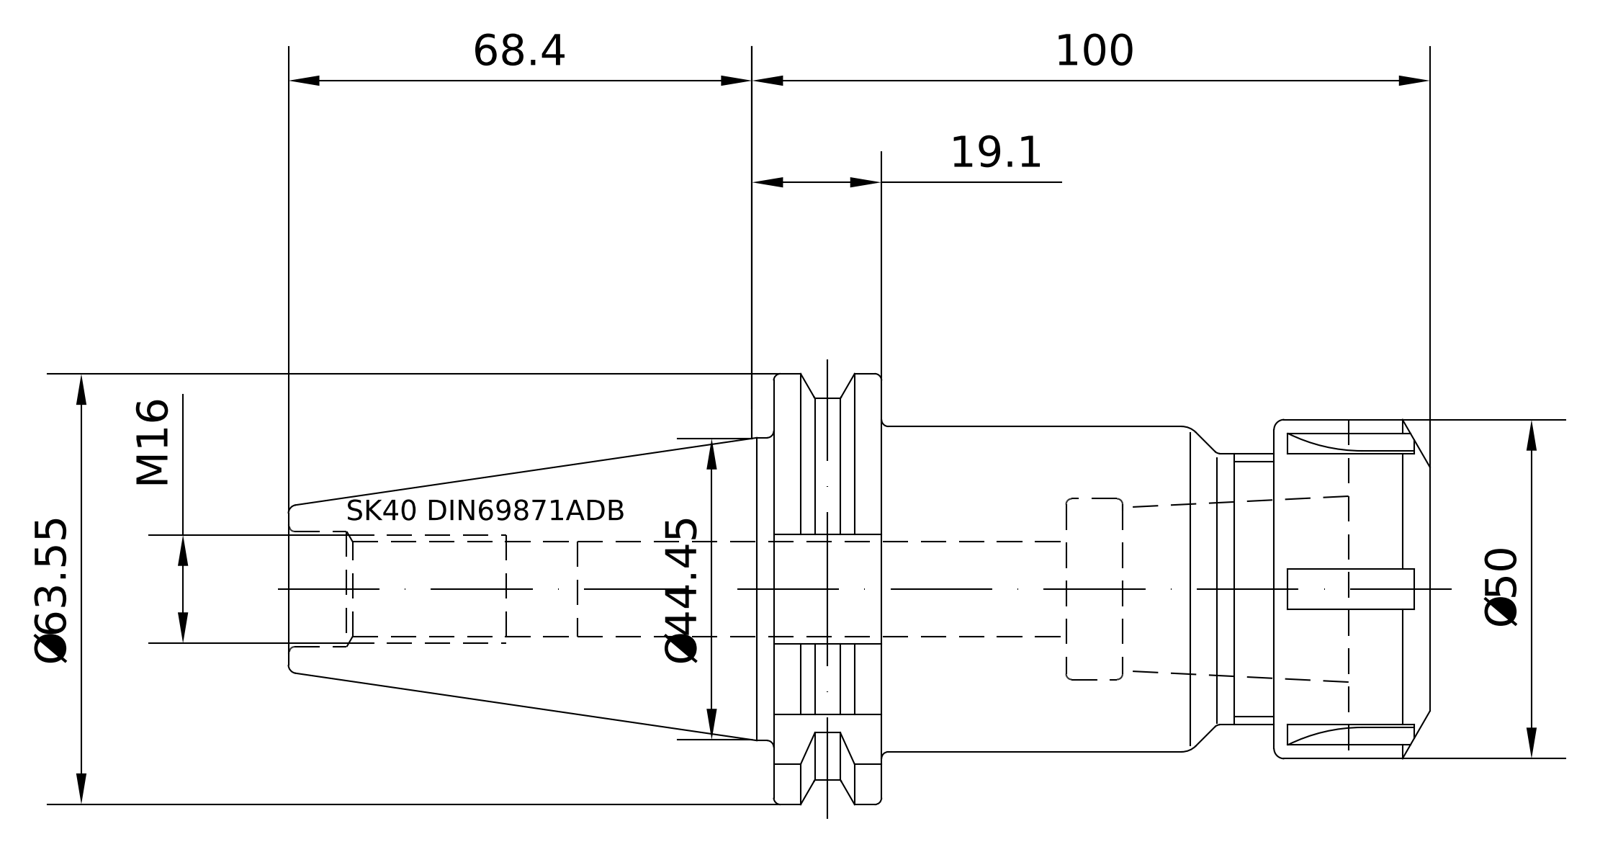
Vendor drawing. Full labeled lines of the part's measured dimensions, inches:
Part name (STEP PRODUCT): 40-321-32; 83-912-32; 40-321-32_ASM
STEP written by: PRO/ENGINEER BY PARAMETRIC TECHNOLOGY CORPORATION, 2010430 (CONFIG_CONTROL_DESIGN)
Units: inches
Bodies: 2 solids, 144 faces (49 planar, 34 cylindrical, 61 other)
Overall size (bounding box): 6.624 × 2.501 × 2.418
Volume: 14.07 in³ · Surface area: 62.49 in²
Round holes (diameter × count): ⌀0.545 ×1, ⌀0.67 ×1, ⌀0.689 ×1, ⌀0.925 ×1
Round bosses / shafts (diameter × count): ⌀1.969 ×1, ⌀1.89 ×1, ⌀1.722 ×1, ⌀1.575 ×1, ⌀0.63 ×1
Partial cylindrical surfaces — rounded edges, fillets, slot ends (radius × count): R0.106 ×6, R0.053 ×1, R1.102 ×1, R1.25 ×1
Main face-to-face distances: 2.925, 3.811, 0.886, 0.624, 2.301, 3.187, 3.299, 2.675, 0.374, 0.512
